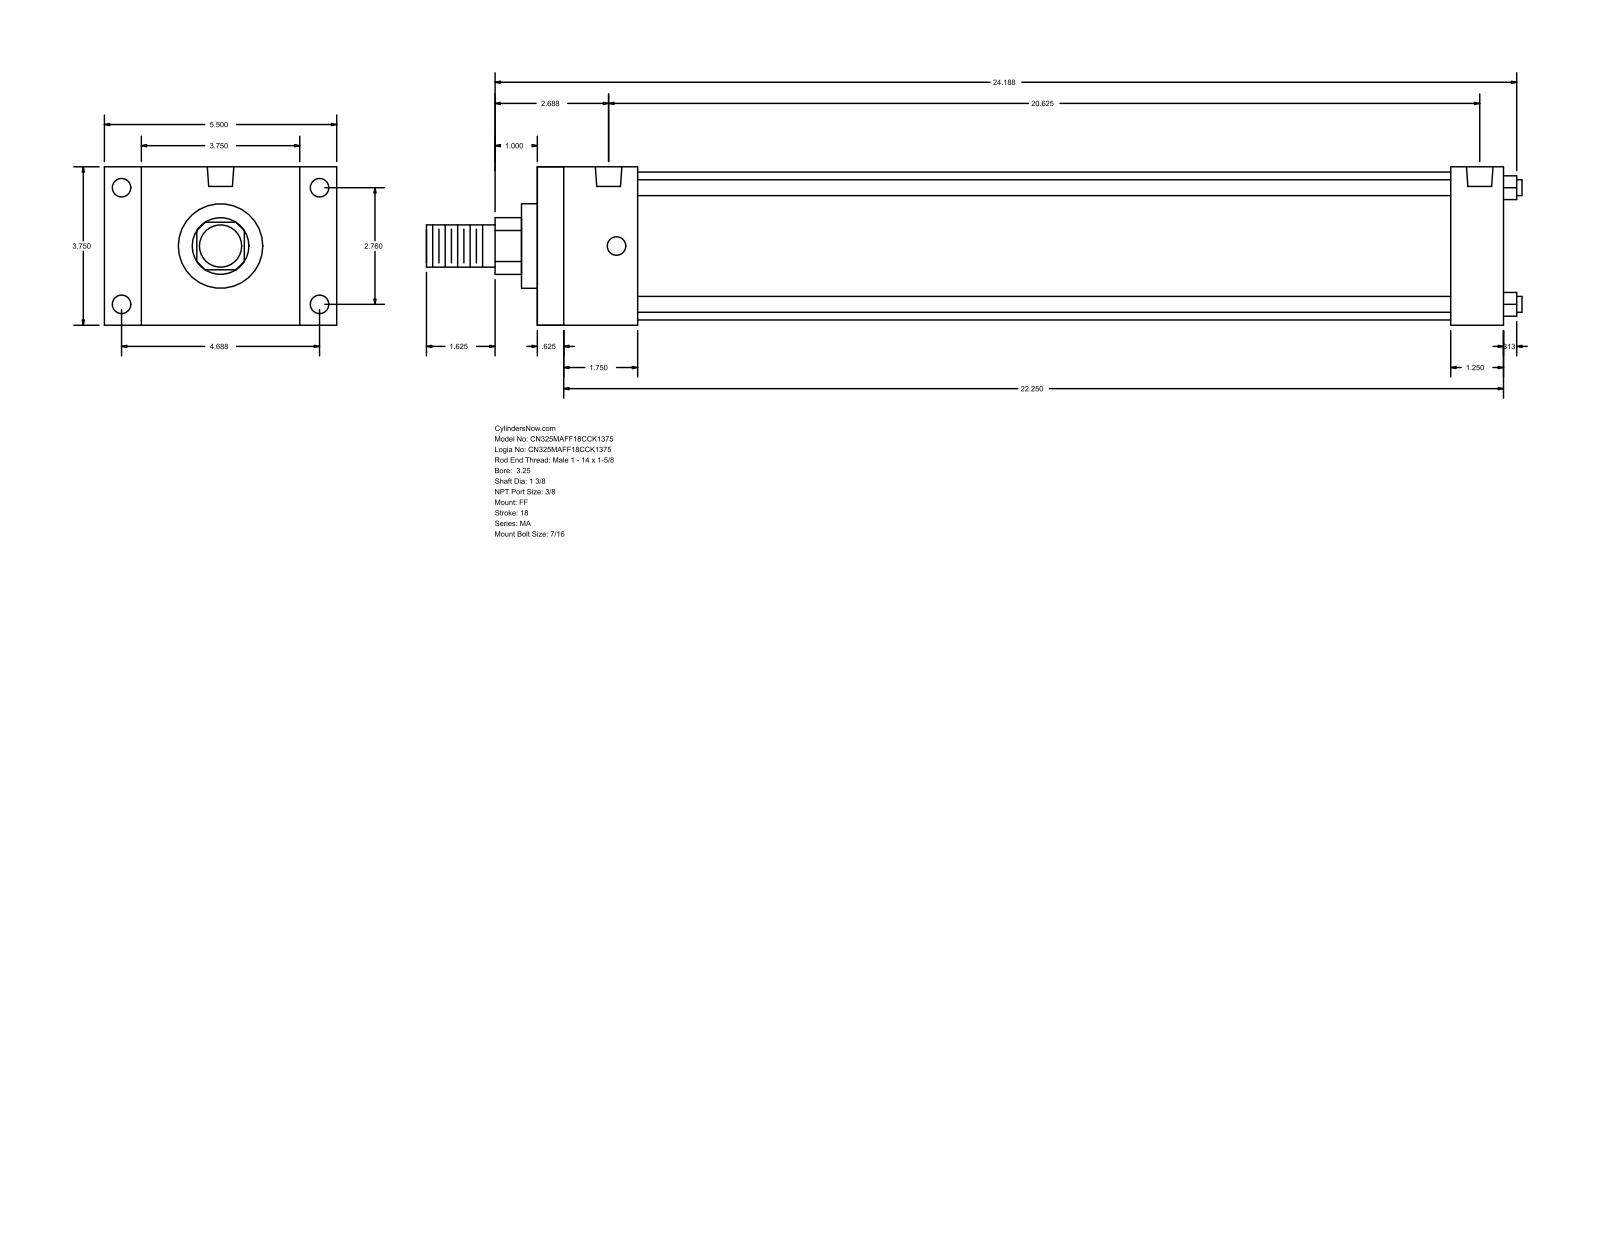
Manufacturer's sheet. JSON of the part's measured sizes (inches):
{"part_name": "MA_FF__0325_1.375", "step_written_by": "GSSL Pune (CONFIG_CONTROL_DESIGN)", "units": "inches", "bodies": {"solids": 0, "faces": 92, "planar": 64, "cylindrical": 28, "other": 0}, "overall_size": [25.937, 5.5, 3.75], "round_holes": [[0.437, 8], [0.627, 2]], "round_bosses_or_shafts": [[0.375, 4], [3.5, 1], [2, 1], [1.375, 1], [1, 1]], "partial_cylinders_radius": [[0.672, 1]], "face_to_face_distances": [3.75, 22.875, 0.625, 22.25, 0.875, 4.625, 2.375, 21.625, 1.75, 21], "hole_center_spacings": [2.76, 4.687, 5.439, 20.25, 0.187, 0.188, 20.437, 20.438]}
